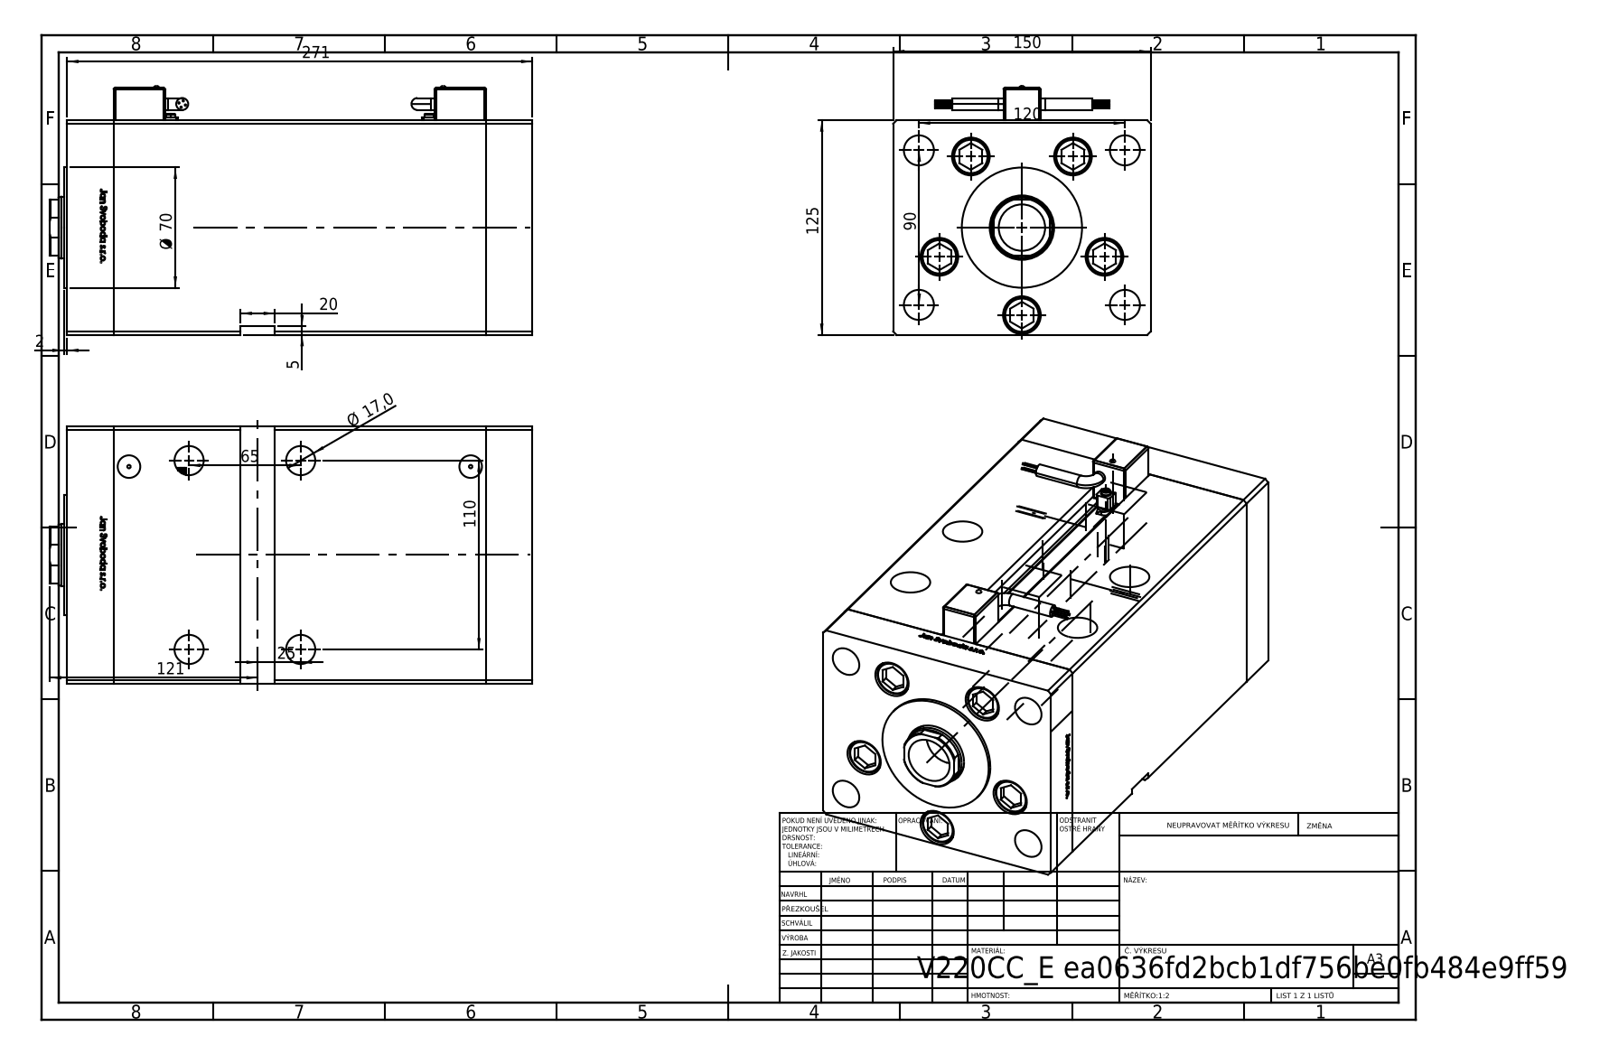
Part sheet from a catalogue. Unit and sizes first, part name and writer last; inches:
Units: inches
Overall size (bounding box): 11.063 × 5.906 × 5.713
Round holes (diameter × count): ⌀0.689 ×9, ⌀0.866 ×5, ⌀0.669 ×4, ⌀0.906 ×4, ⌀0.079 ×2, ⌀0.142 ×2, ⌀0.197 ×2, ⌀0.276 ×2, ⌀0.518 ×2, ⌀1.063 ×1, ⌀1.417 ×1, ⌀1.476 ×1
Round bosses / shafts (diameter × count): ⌀0.033 ×8, ⌀0.827 ×5, ⌀0.315 ×5, ⌀0.276 ×4, ⌀0.236 ×2, ⌀0.138 ×2, ⌀0.098 ×2, ⌀2.756 ×1
Partial cylindrical surfaces — rounded edges, fillets, slot ends (radius × count): R0.039 ×24, R0.157 ×4, R0.037 ×2, R0.689 ×1
Main face-to-face distances: 5.906, 4.921, 8.543, 1.063, 9.606, 10.669, 3.701, 2.638, 0.256, 4.724
Hole centre spacings: 2.008, 2.953, 0.325, 1.198, 1.2, 2.123, 2.206, 2.241
Volume: 255.8 in³ · Surface area: 692.3 in²
Bodies: 16 solids, 1410 faces (551 planar, 251 cylindrical, 608 other)
Part name (STEP PRODUCT): V220C_E_VC; V220C BACK_E; V220C_E MIDDLE; Magnetic_Switch_MSU4 (+2 more)
STEP written by: SolidWorks 2019 (CONFIG_CONTROL_DESIGN)
